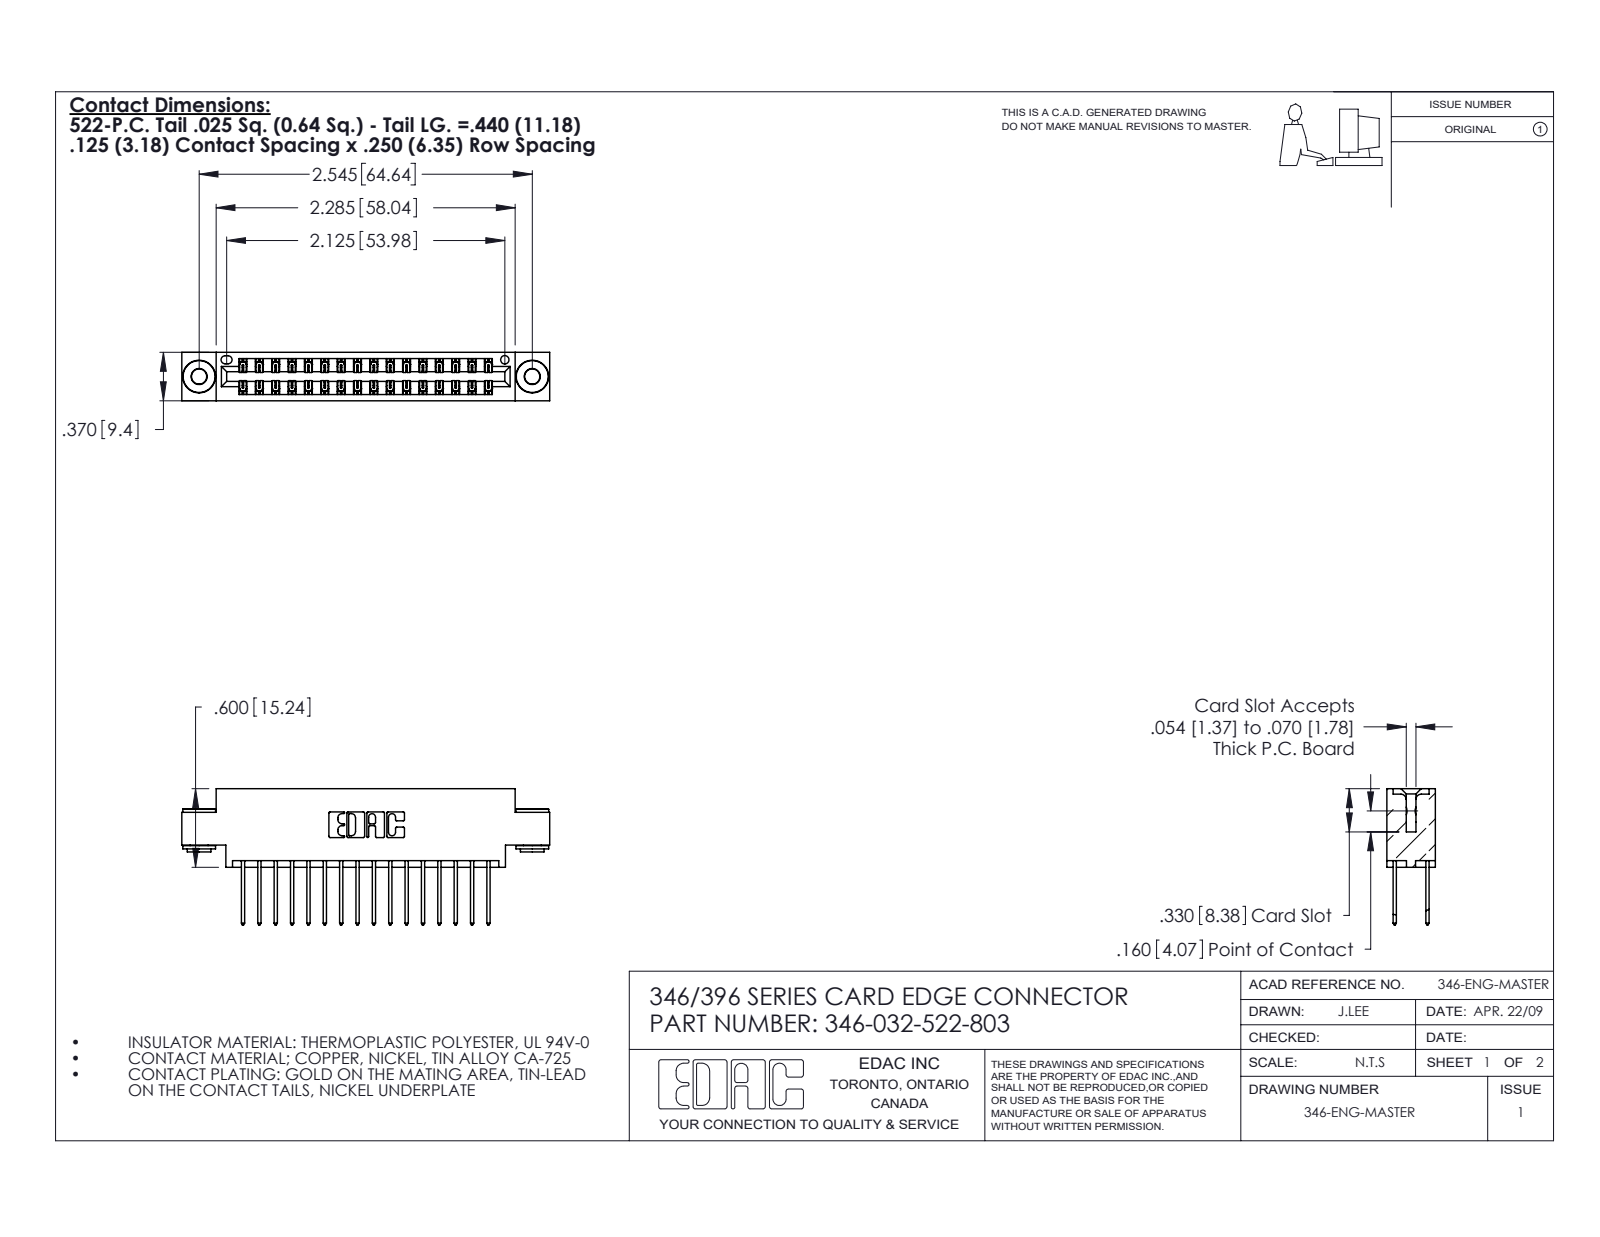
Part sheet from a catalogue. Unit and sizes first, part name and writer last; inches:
Units: inches
Overall size (bounding box): 2.81 × 1.04 × 0.37
Round holes (diameter × count): ⌀0.116 ×2, ⌀0.156 ×2, ⌀0.064 ×1
Round bosses / shafts (diameter × count): ⌀0.25 ×2, ⌀0.18 ×2, ⌀0.136 ×2
Partial cylindrical surfaces — rounded edges, fillets, slot ends (radius × count): R0.006 ×48, R0.01 ×32, R0.01 ×22, R0.007 ×6, R0.031 ×6, R0.026 ×3, R0.014 ×2, R0.022 ×2
Main face-to-face distances: 0.048, 0.322, 0.25, 0.37, 0.025, 0.072, 0.298, 0.275, 0.222, 0.148
Hole centre spacings: 0.246, 2.338, 2.545
Volume: 0.408 in³ · Surface area: 14.87 in²
Bodies: 35 solids, 1842 faces (1224 planar, 610 cylindrical, 8 other)
Part name (STEP PRODUCT): 345-292-001_345-293-122; 345-250-002_345-250-002-102; 346 Part_0.170 Offset - 0.156 Dia-TH; 346-032-522-803
STEP written by: SolidWorks 2020 (CONFIG_CONTROL_DESIGN)
